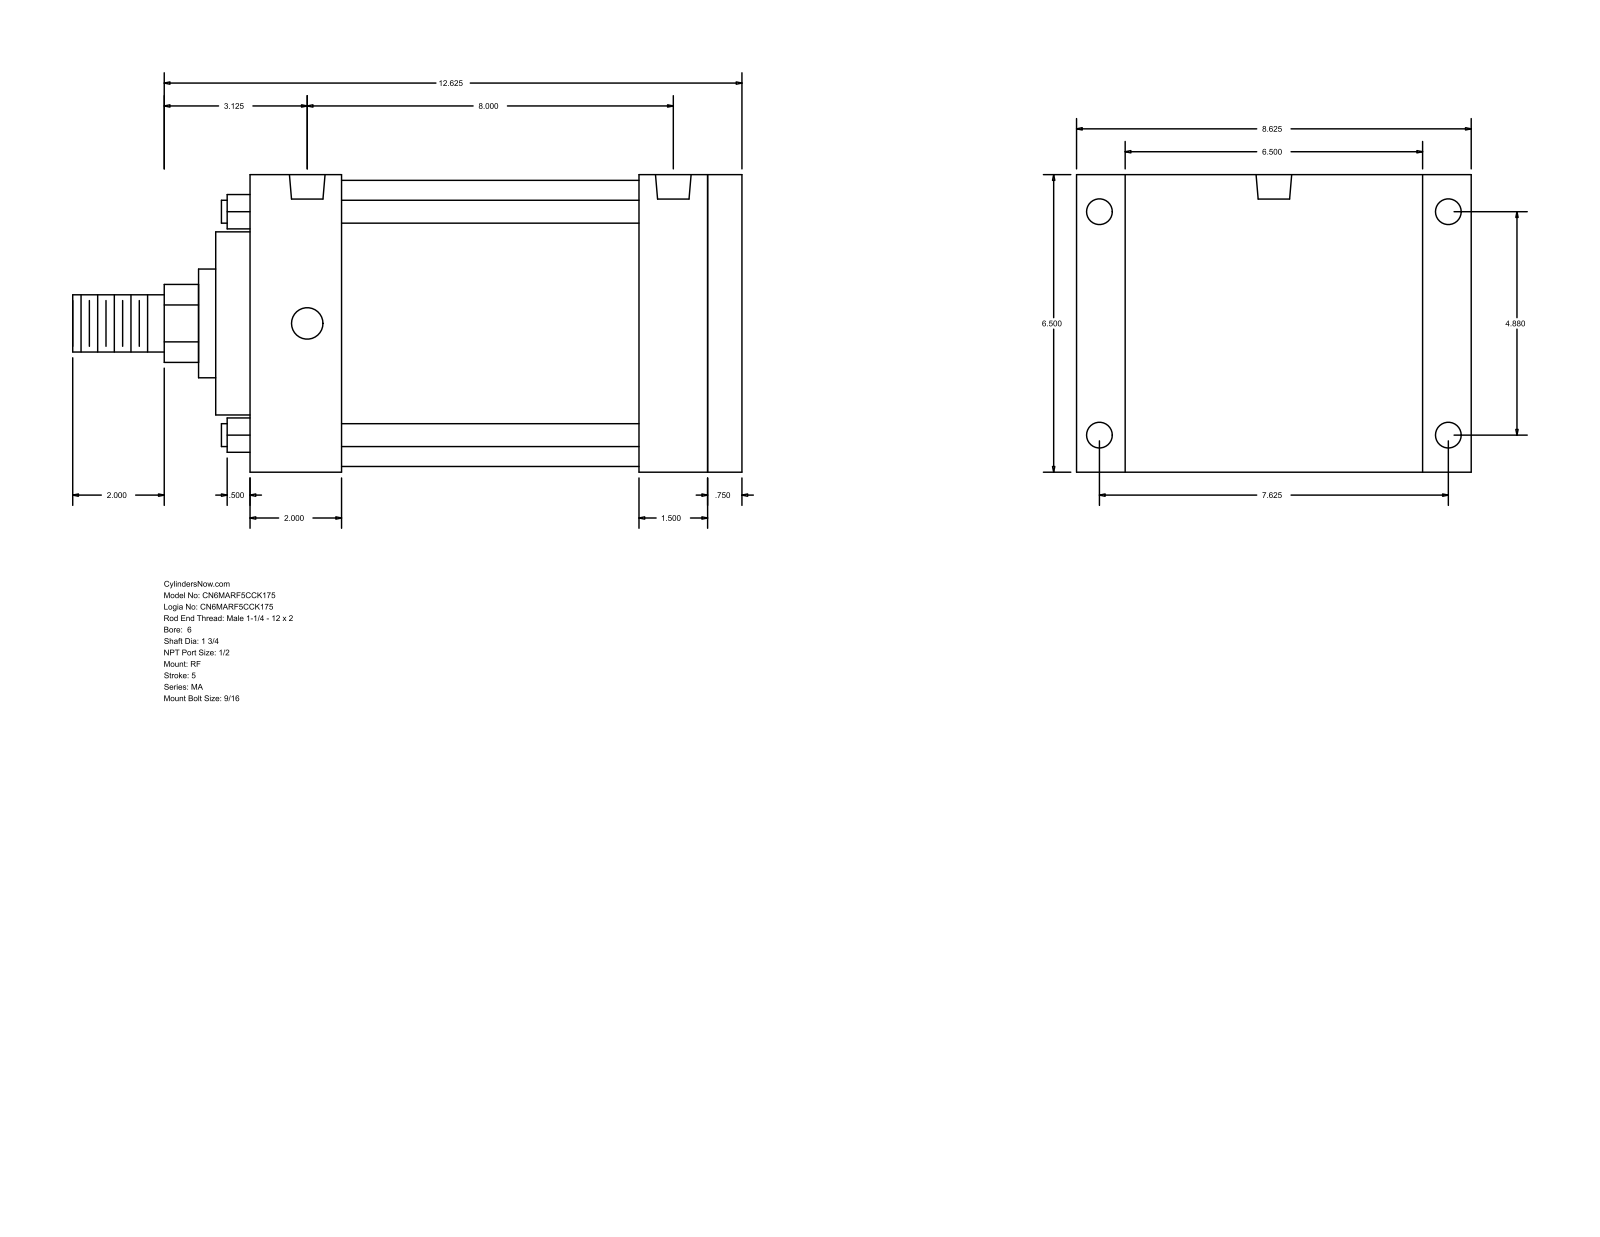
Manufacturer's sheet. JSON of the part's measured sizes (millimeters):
{"part_name": "MA_RF__0600_1.75", "step_written_by": "GSSL Pune (CONFIG_CONTROL_DESIGN)", "units": "millimeters", "bodies": {"solids": 0, "faces": 94, "planar": 65, "cylindrical": 29, "other": 0}, "overall_size": [371.48, 219.07, 165.1], "round_holes": [[14.29, 4], [17.46, 4], [19.77, 2]], "round_bosses_or_shafts": [[12.7, 4], [158.75, 1], [101.6, 1], [60.33, 1], [44.45, 1], [31.75, 1]], "partial_cylinders_radius": [[21.63, 1]], "face_to_face_distances": [165.1, 273.06, 254, 19.06, 38.1, 50.8, 19.05, 203.2, 222.26, 215.9], "hole_center_spacings": [123.96, 193.68, 203.19, 229.95]}
